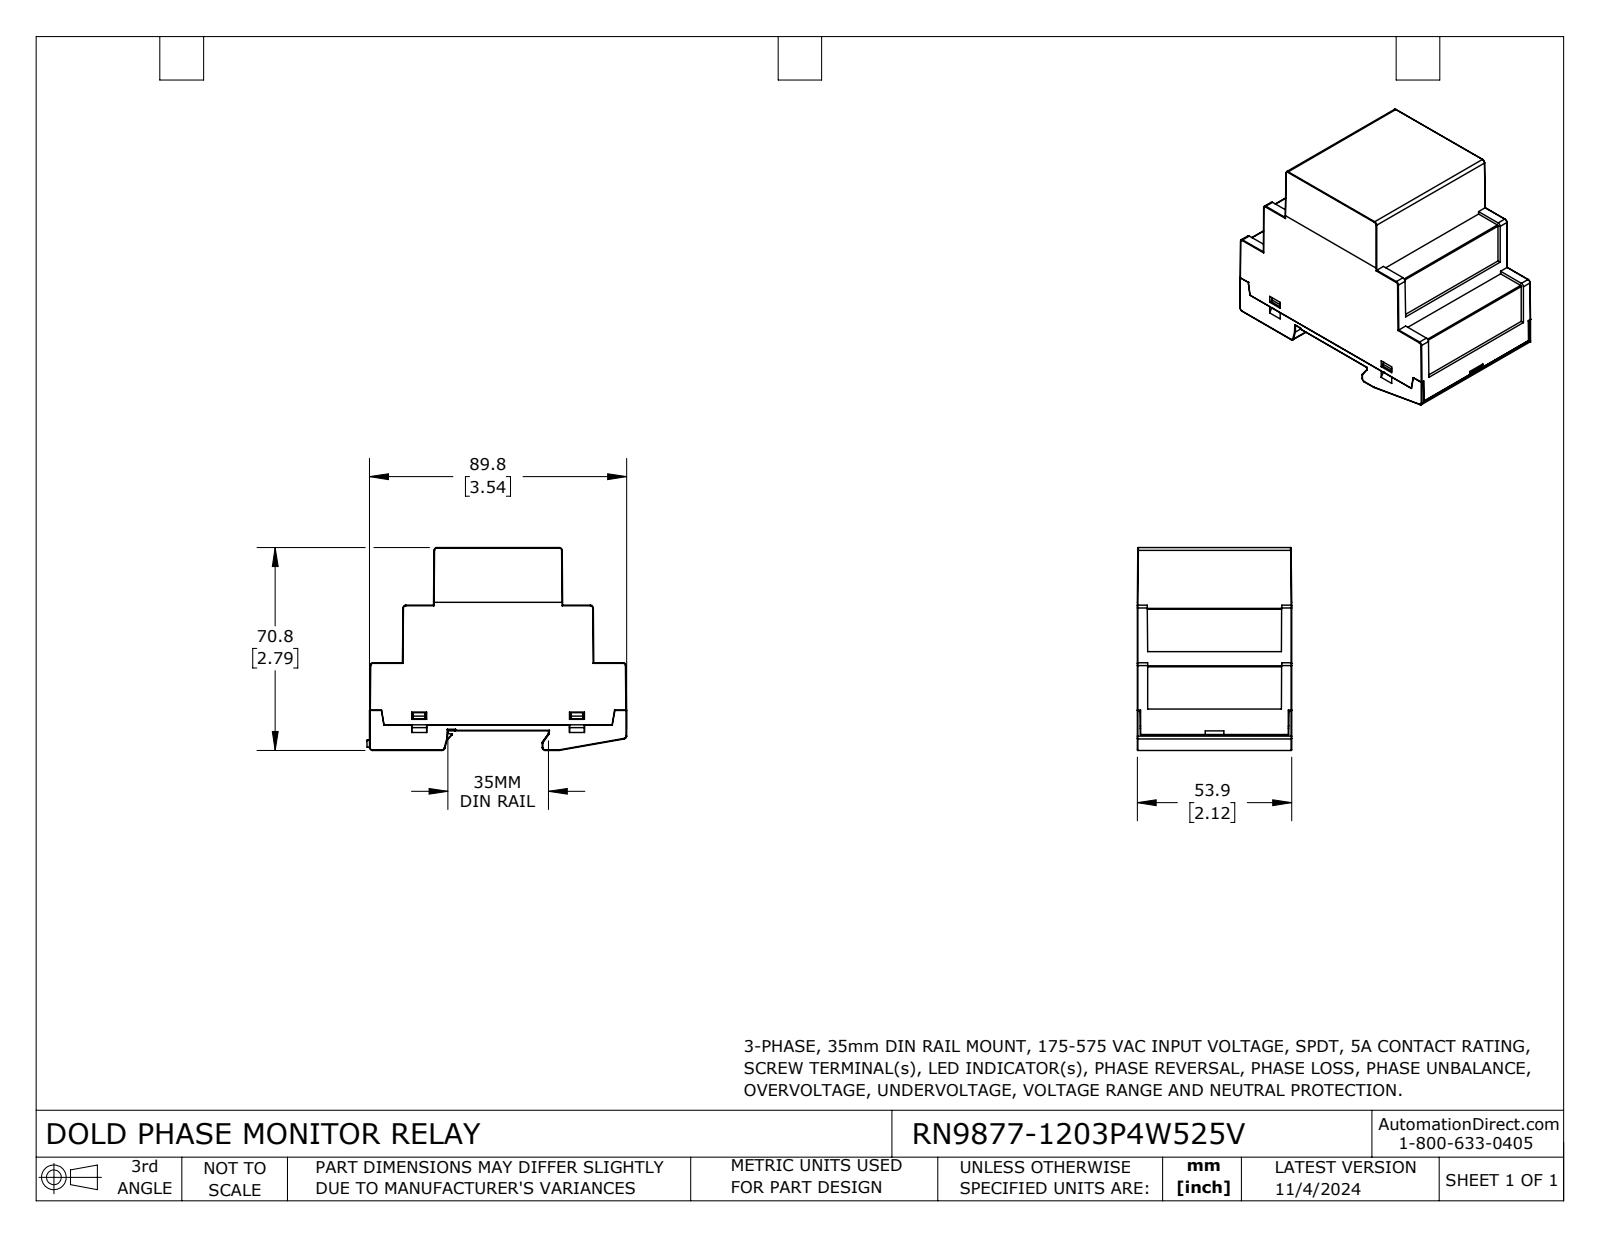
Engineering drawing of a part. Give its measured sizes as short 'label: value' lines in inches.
name: RN9877-1203P4W525V
written by: SolidWorks 2023 (CONFIG_CONTROL_DESIGN)
unit: in
bodies: 3 solids, 1027 faces (823 planar, 126 cylindrical, 78 other)
size: 3.572 × 2.787 × 2.122
volume: 13.92 in³; area: 70.57 in²
bosses: 5× ⌀0.098, 1× ⌀0.181
rounds: 44× R0.008, 18× R0.039, 11× R0.02, 9× R0.004, 4× R0.012, 2× R0.016, 1× R0.011, 1× R0.028
face distances: 2.122, 2.435, 0.041, 0.085, 2.52, 0.217, 0.352, 0.26, 0.175, 2.26
